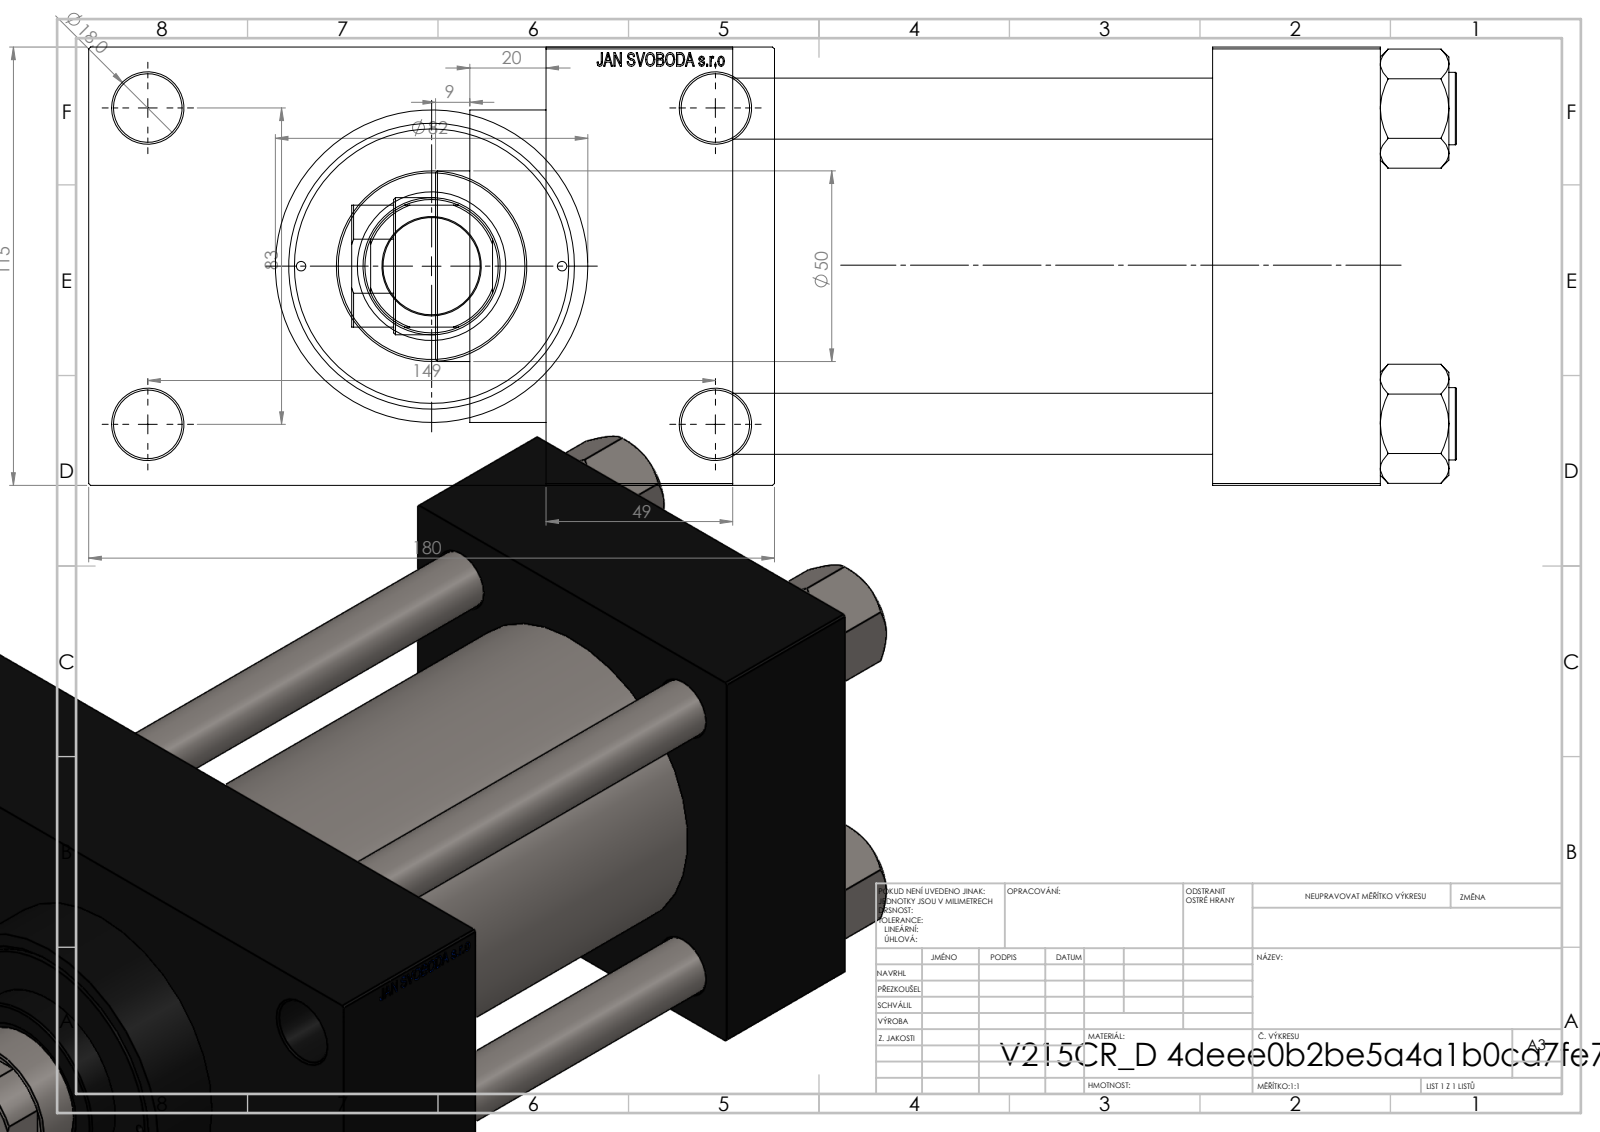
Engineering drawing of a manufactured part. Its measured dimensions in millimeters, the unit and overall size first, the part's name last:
Units: millimetres
Overall size (bounding box): 290 × 180 × 115
Round holes (diameter × count): ⌀16 ×4, ⌀18 ×4, ⌀2.5 ×2, ⌀7 ×2, ⌀26.44 ×2, ⌀35 ×2, ⌀25.5 ×1, ⌀36 ×1, ⌀39 ×1, ⌀61 ×1, ⌀72 ×1, ⌀80 ×1
Round bosses / shafts (diameter × count): ⌀19 ×4, ⌀86 ×1, ⌀82 ×1, ⌀50 ×1
Partial cylindrical surfaces — rounded edges, fillets, slot ends (radius × count): R17.5 ×1
Main face-to-face distances: 115, 126, 175, 49, 170, 44, 219, 32.5, 147.5, 180
Hole centre spacings: 33.15, 41.96, 57.81, 58.48, 82.7, 85.28, 86.17, 89.24
Volume: 2 135 000 mm³ · Surface area: 346 617 mm²
Bodies: 11 solids, 1159 faces (547 planar, 92 cylindrical, 520 other)
Part name (STEP PRODUCT): V215_VC_A; NUT_M5_D; V215CR_D_TYCINKA; V215CR_VCP_D (+1 more)
STEP written by: SolidWorks 2019 (CONFIG_CONTROL_DESIGN)
